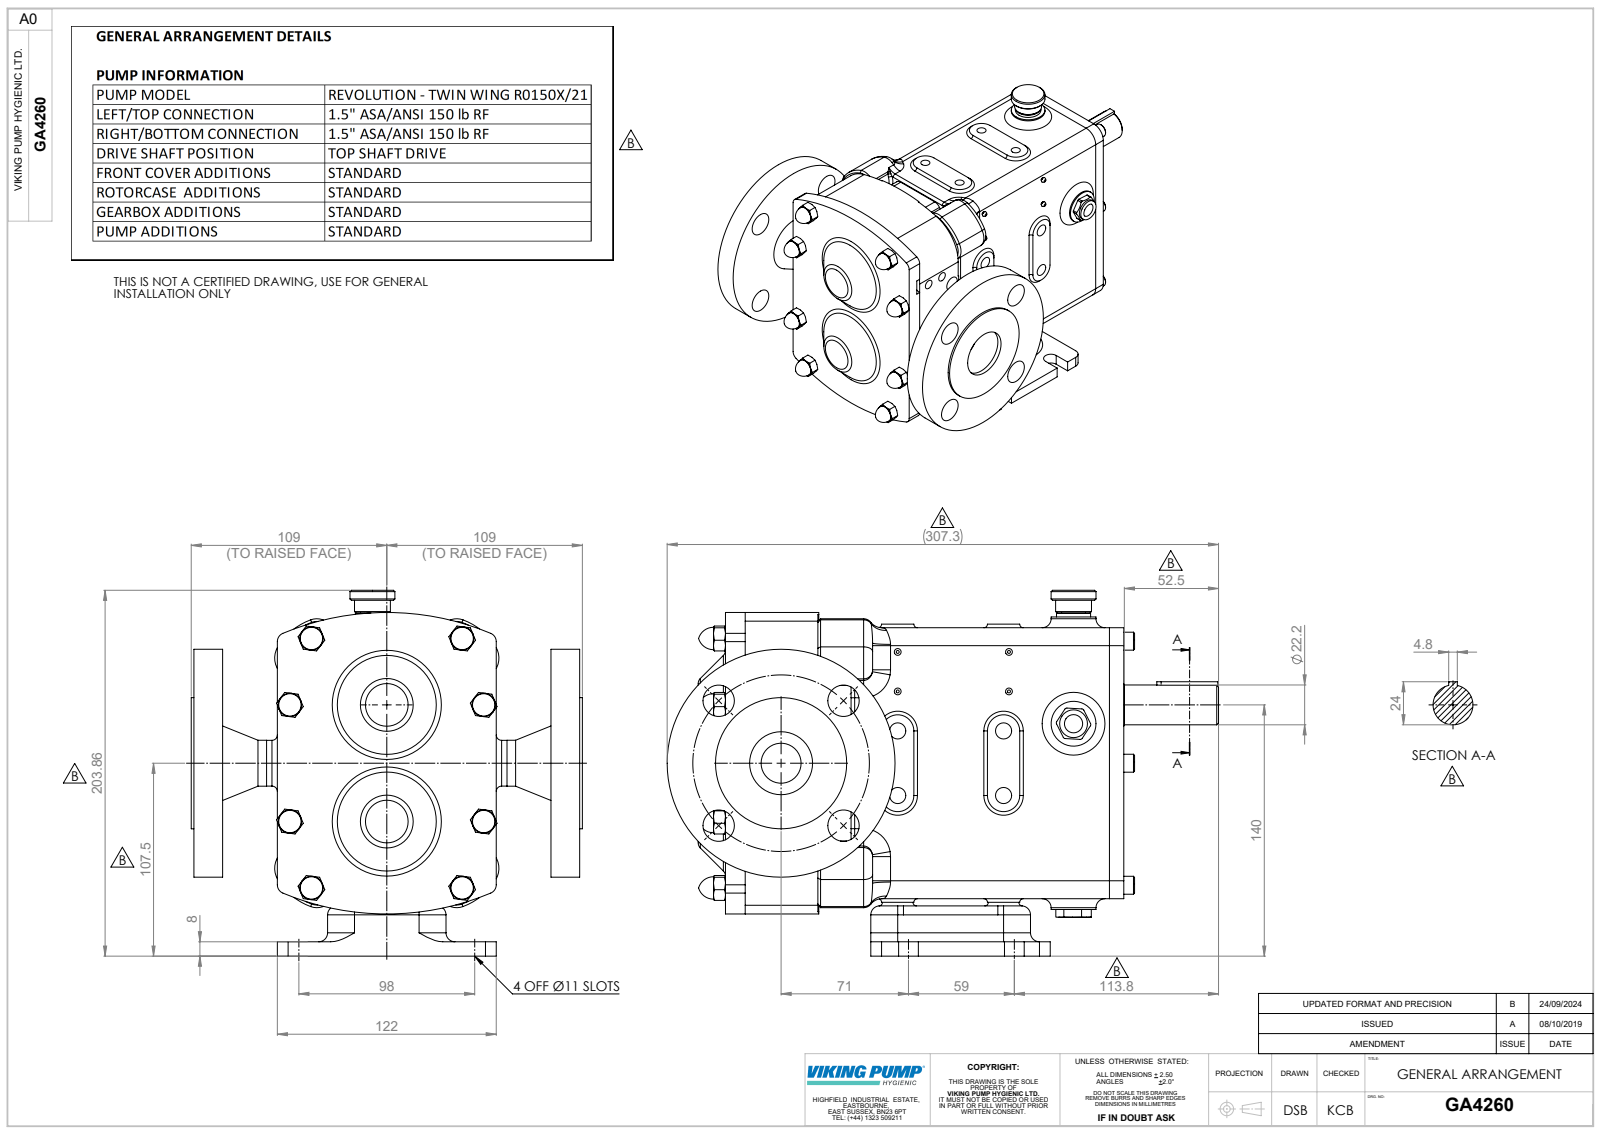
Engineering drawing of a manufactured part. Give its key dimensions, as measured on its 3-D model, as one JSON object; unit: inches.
{"part_name": "Copy of Z94-5301-12 - 1.5 Inch to 1 Inch W-Neck^GA4260; GA4260; Copy of R0150 CPP H TSD^GA4260", "step_written_by": "SolidWorks 2023 (AUTOMOTIVE_DESIGN)", "units": "inches", "bodies": {"solids": 3, "faces": 1249, "planar": 367, "cylindrical": 353, "other": 529}, "overall_size": [12.098, 8.583, 8.026], "volume_in3": 233.6, "surface_area_in2": 462.2, "round_holes": [[0.268, 4], [0.276, 4], [0.354, 4], [0.689, 4], [0.433, 2], [0.878, 1], [0.887, 1], [1.382, 1]], "round_bosses_or_shafts": [[0.394, 6], [0.984, 4], [0.512, 4], [5, 1], [2.878, 1], [1.008, 1], [1.004, 1], [0.985, 1]], "partial_cylinders_radius": [[0.079, 28], [0.394, 26], [0.197, 19], [0.236, 14], [0.315, 8], [0.05, 6], [1.22, 6], [0.049, 4]], "face_to_face_distances": [5.295, 1.909, 0.63, 7.205, 2.539, 3.386, 5.925, 7.835, 1.831, 6.004], "hole_center_spacings": [1.417, 1.937, 2.323, 2.721, 2.739, 0.551, 0.613, 0.824]}
